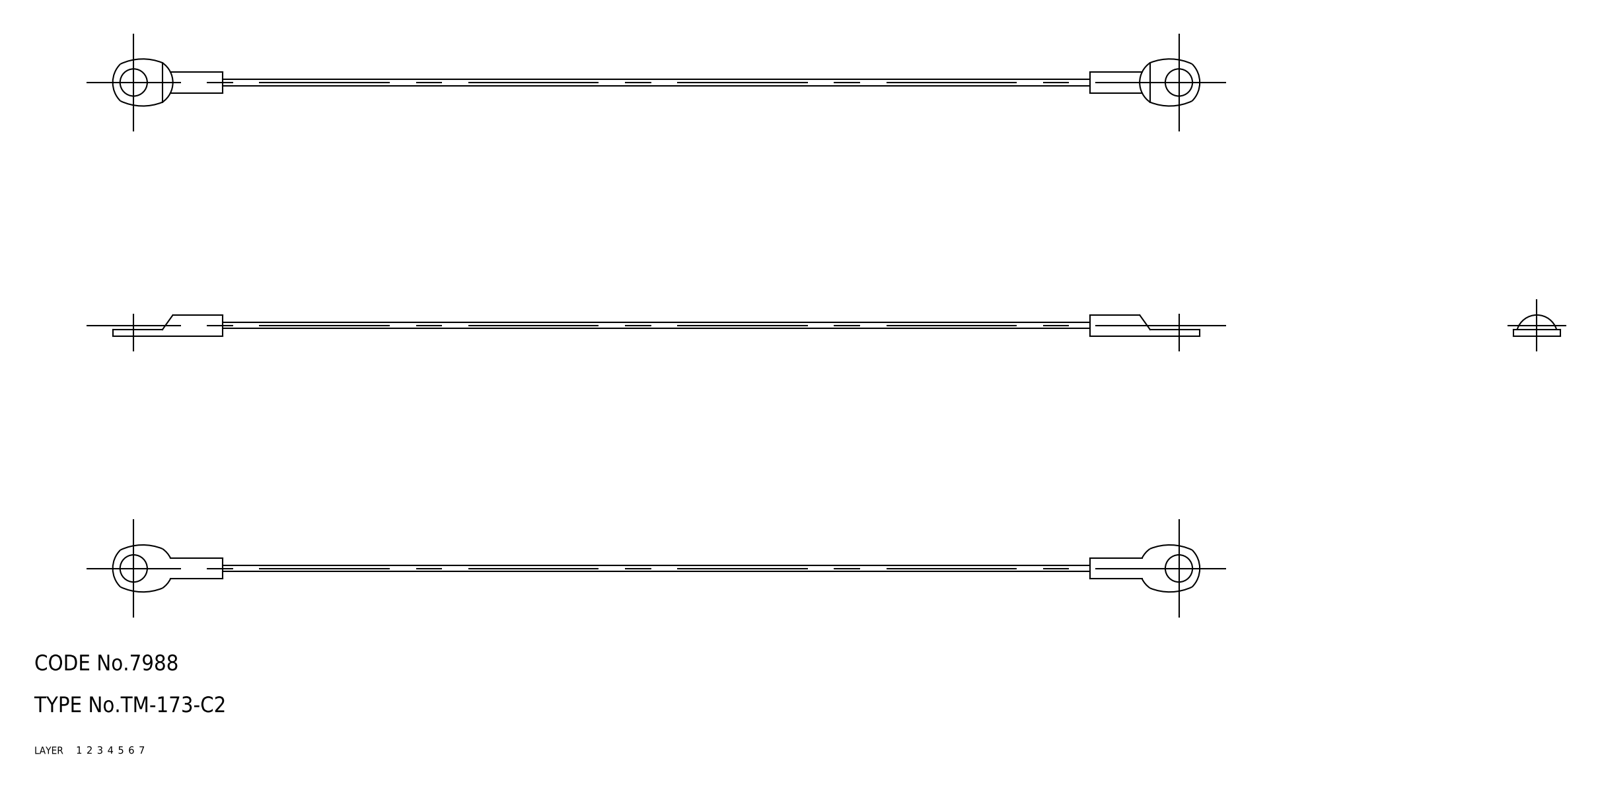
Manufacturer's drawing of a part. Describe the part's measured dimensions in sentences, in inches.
The part is named "terminal; wire; TM_173_C2_28492_36". Its 3-D file was written by "CADfix (AUTOMOTIVE_DESIGN)". It is 3 solids with 56 faces: 0 planar, 0 cylindrical and 56 other. Overall it measures 8.189 by 0.354 by 0.157 inches. Its volume is 0.036 cubic inches and its surface area 2.181 square inches.
